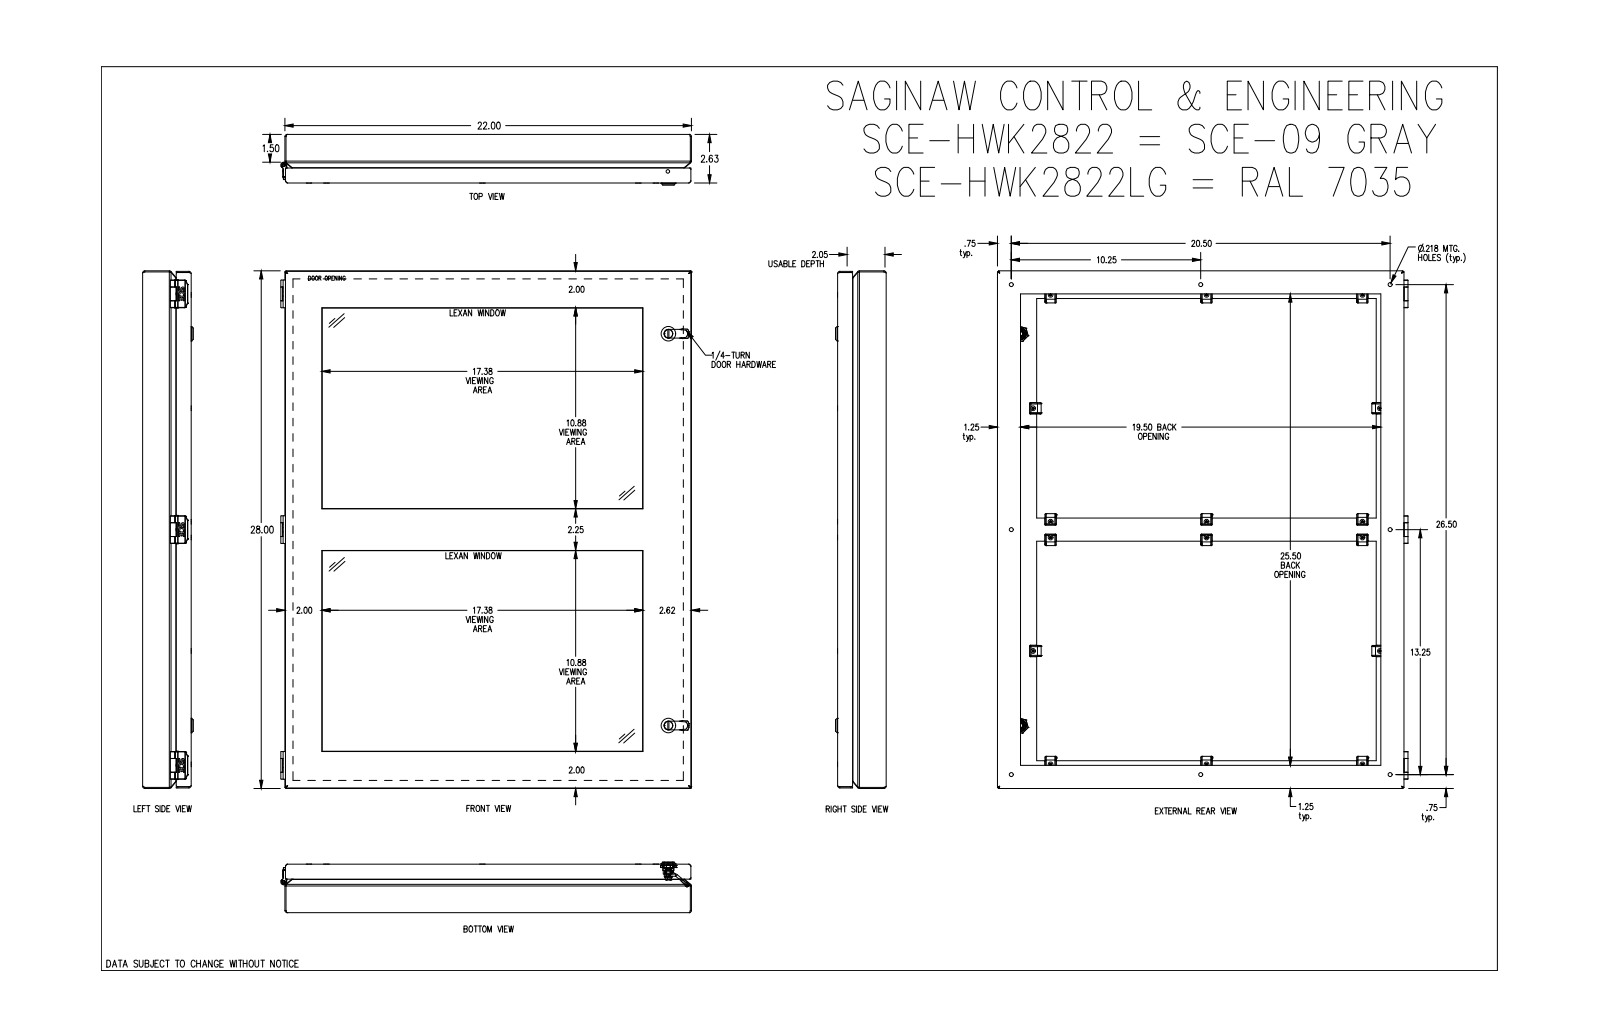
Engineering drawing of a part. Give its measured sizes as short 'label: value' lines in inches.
name: SCE-HWK2822
written by: SolidWorks 2021 (AUTOMOTIVE_DESIGN)
unit: in
bodies: 84 solids, 3389 faces (1422 planar, 939 cylindrical, 1028 other)
size: 28.06 × 22.22 × 2.733
volume: 167.2 in³; area: 3 063 in²
holes: 16× ⌀0.138, 16× ⌀0.156, 16× ⌀0.213, 8× ⌀0.218, 3× ⌀0.164, 3× ⌀0.17, 3× ⌀0.174, 3× ⌀0.266, 3× ⌀0.338, 2× ⌀0.2, 2× ⌀0.239, 2× ⌀0.254
bosses: 16× ⌀0.262, 16× ⌀0.212, 3× ⌀0.479, 3× ⌀0.26, 3× ⌀0.15, 2× ⌀0.788, 2× ⌀0.548, 2× ⌀0.46
rounds: 99× R0.106, 64× R0.05, 54× R0.005, 48× R0.008, 44× R0.02, 18× R0.025, 16× R0.01, 16× R0.06
face distances: 0.06, 0.181, 0.241, 0.236, 0.055, 0.059, 0.09, 0.031, 2.385, 2.566
hole spacings: 6.208, 11.212, 13.125, 18.849, 12.27, 7.054, 8.437, 8.438
